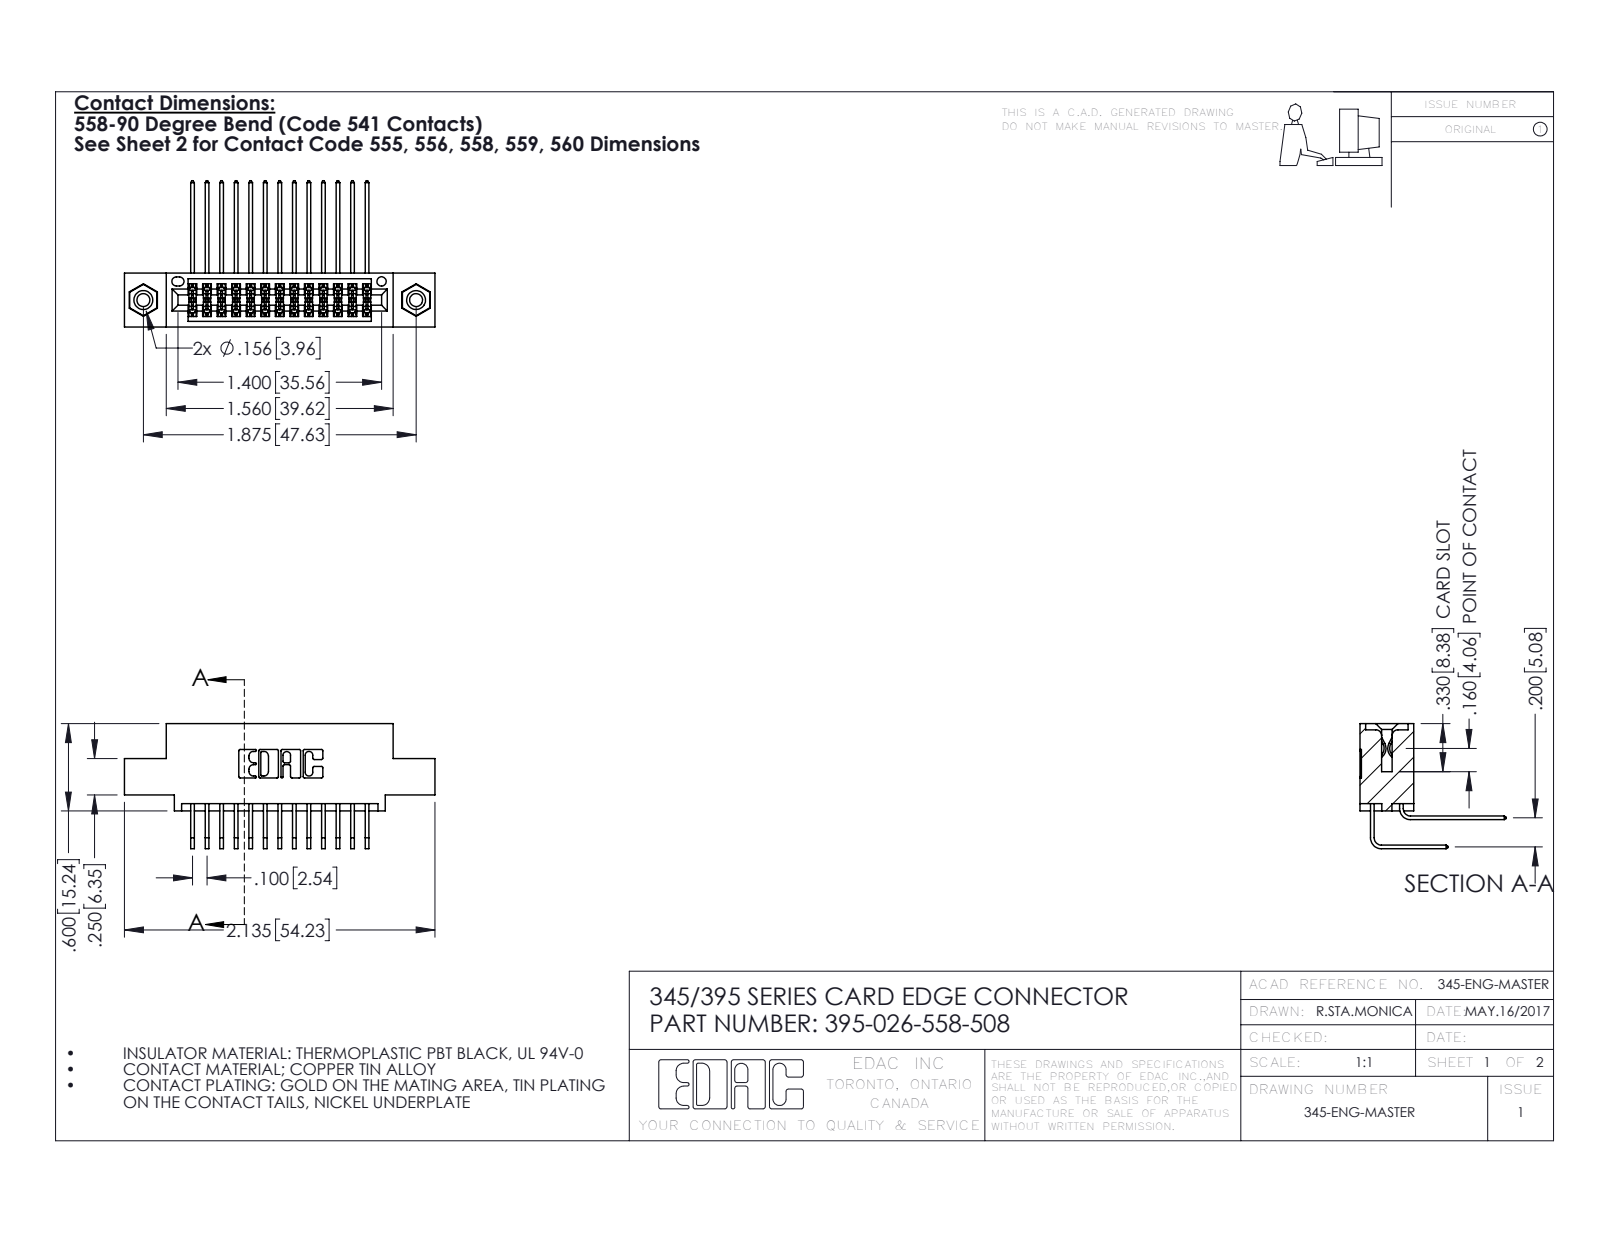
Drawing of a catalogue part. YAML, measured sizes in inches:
part_name: "345 Part_0.110 Offset - 0.156 Dia-TI; 345-292-001_558 559 Tail - 1; 395-026-558-508; 345-250-001_345-250-003-102 (+1 more)"
step_written_by: "SolidWorks 2016 (CONFIG_CONTROL_DESIGN)"
units: inches
bodies: {solids: 29, faces: 1542, planar: 1026, cylindrical: 500, other: 16}
overall_size: [2.135, 1.005, 0.859]
volume: 0.309
surface_area: 12
round_holes:
  - {diameter: 0.089, count: 2}
  - {diameter: 0.125, count: 2}
  - {diameter: 0.156, count: 2}
  - {diameter: 0.064, count: 1}
round_bosses_or_shafts:
  - {diameter: 0.155, count: 2}
partial_cylinders:
  - {radius: 0.006, count: 40}
  - {radius: 0.01, count: 22}
  - {radius: 0.007, count: 6}
  - {radius: 0.031, count: 6}
  - {radius: 0.026, count: 3}
  - {radius: 0.014, count: 2}
  - {radius: 0.019, count: 2}
  - {radius: 0.022, count: 2}
face_to_face_distances: [0.2, 0.072, 0.298, 0.37, 0.098, 0.272, 0.025, 0.225, 0.1, 0.16]
hole_center_spacings: [0.27, 1.643, 1.875]
